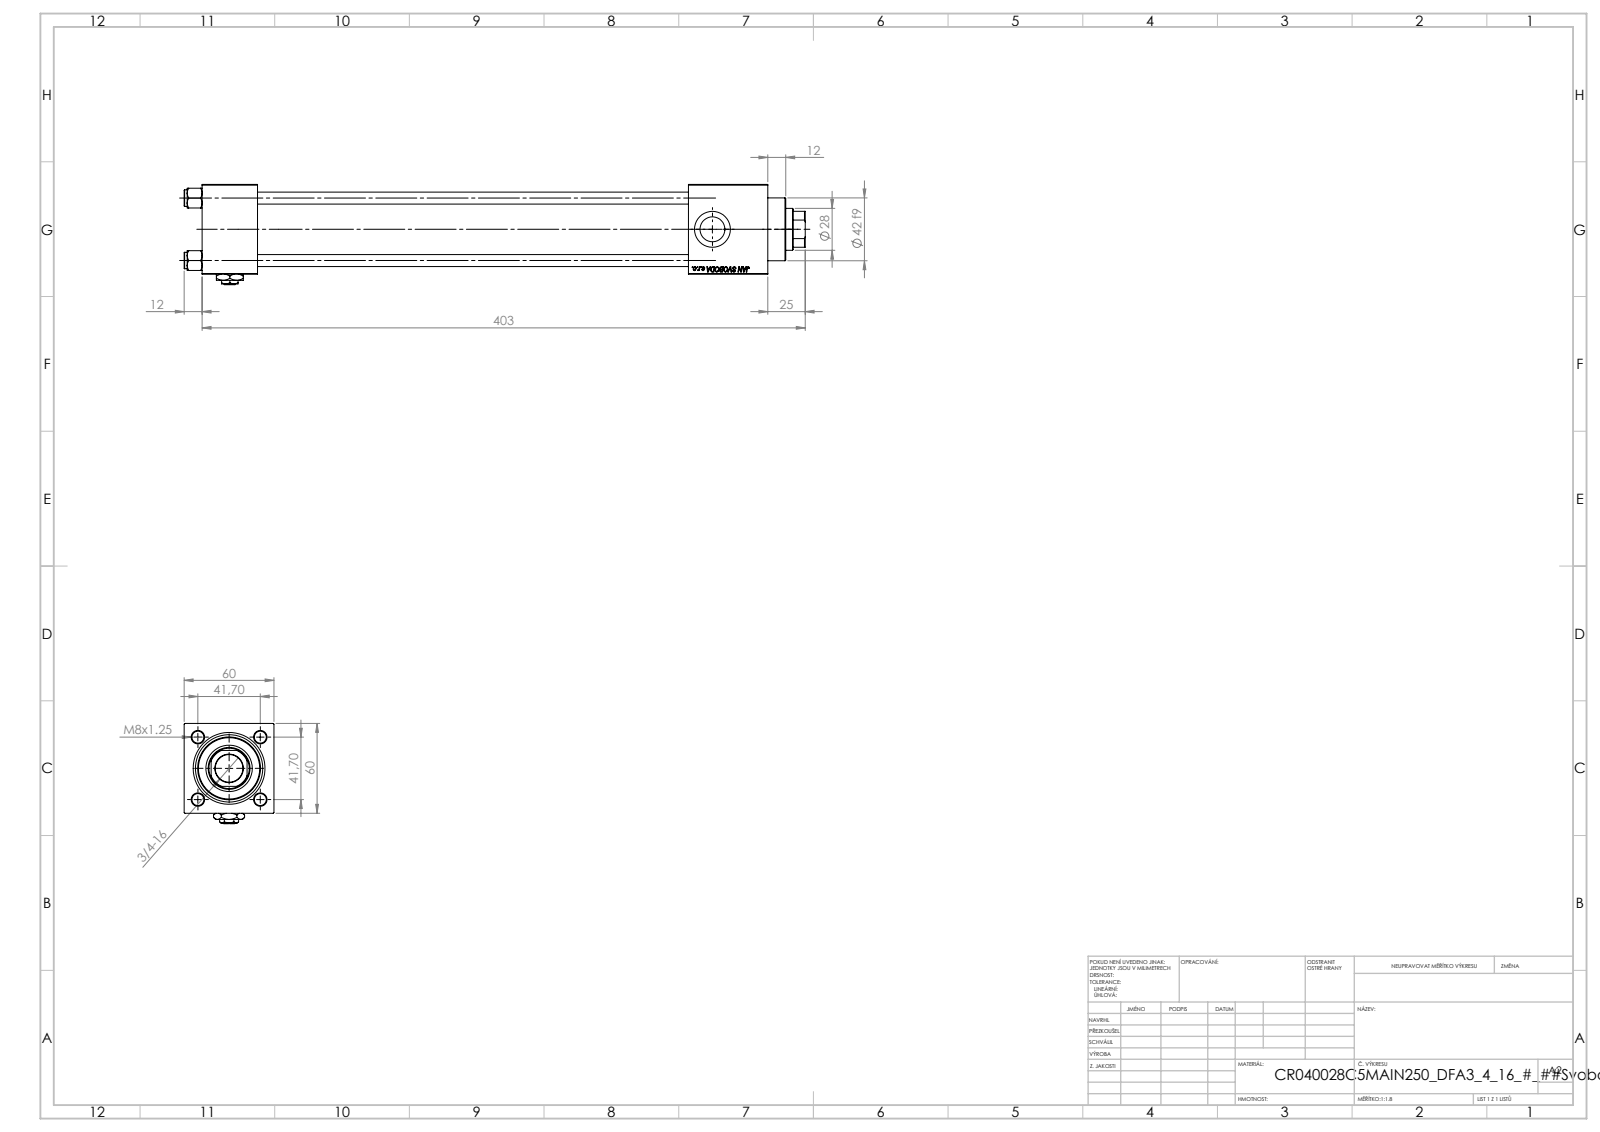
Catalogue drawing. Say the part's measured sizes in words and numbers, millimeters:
The part is named "V215CR_C_TYCINKA; V215CR_VCP_C; NUT_M5_C; V215CR_C_Body (+3 more)". Its 3-D file was written by "SolidWorks 2019 (CONFIG_CONTROL_DESIGN)". It is 13 solids with 1235 faces: 562 planar, 103 cylindrical and 570 other. Overall it measures 415 by 67 by 60 millimeters. Its volume is 727 709 cubic millimeters and its surface area 226 319 square millimeters. Round holes: 4 of diameter 8, 2 of diameter 7, 2 of diameter 16.66, 2 of diameter 24, 1 of diameter 18.5, 1 of diameter 28, 1 of diameter 31, 1 of diameter 40, 1 of diameter 45. Round bosses or shafts: 4 of diameter 11, 1 of diameter 46, 1 of diameter 42, 1 of diameter 36, 1 of diameter 30, 1 of diameter 20, 1 of diameter 18. Partial cylindrical surfaces (rounded edges, fillets, slot ends): 1 of radius 7.5, 1 of radius 12, 1 of radius 13.5. The main face-to-face distances are 60, 37, 325, 288, 349.3, 312.3, 24.3, 53, 378, 341. The hole center spacings are 29.49, 41.7, 58.97.
